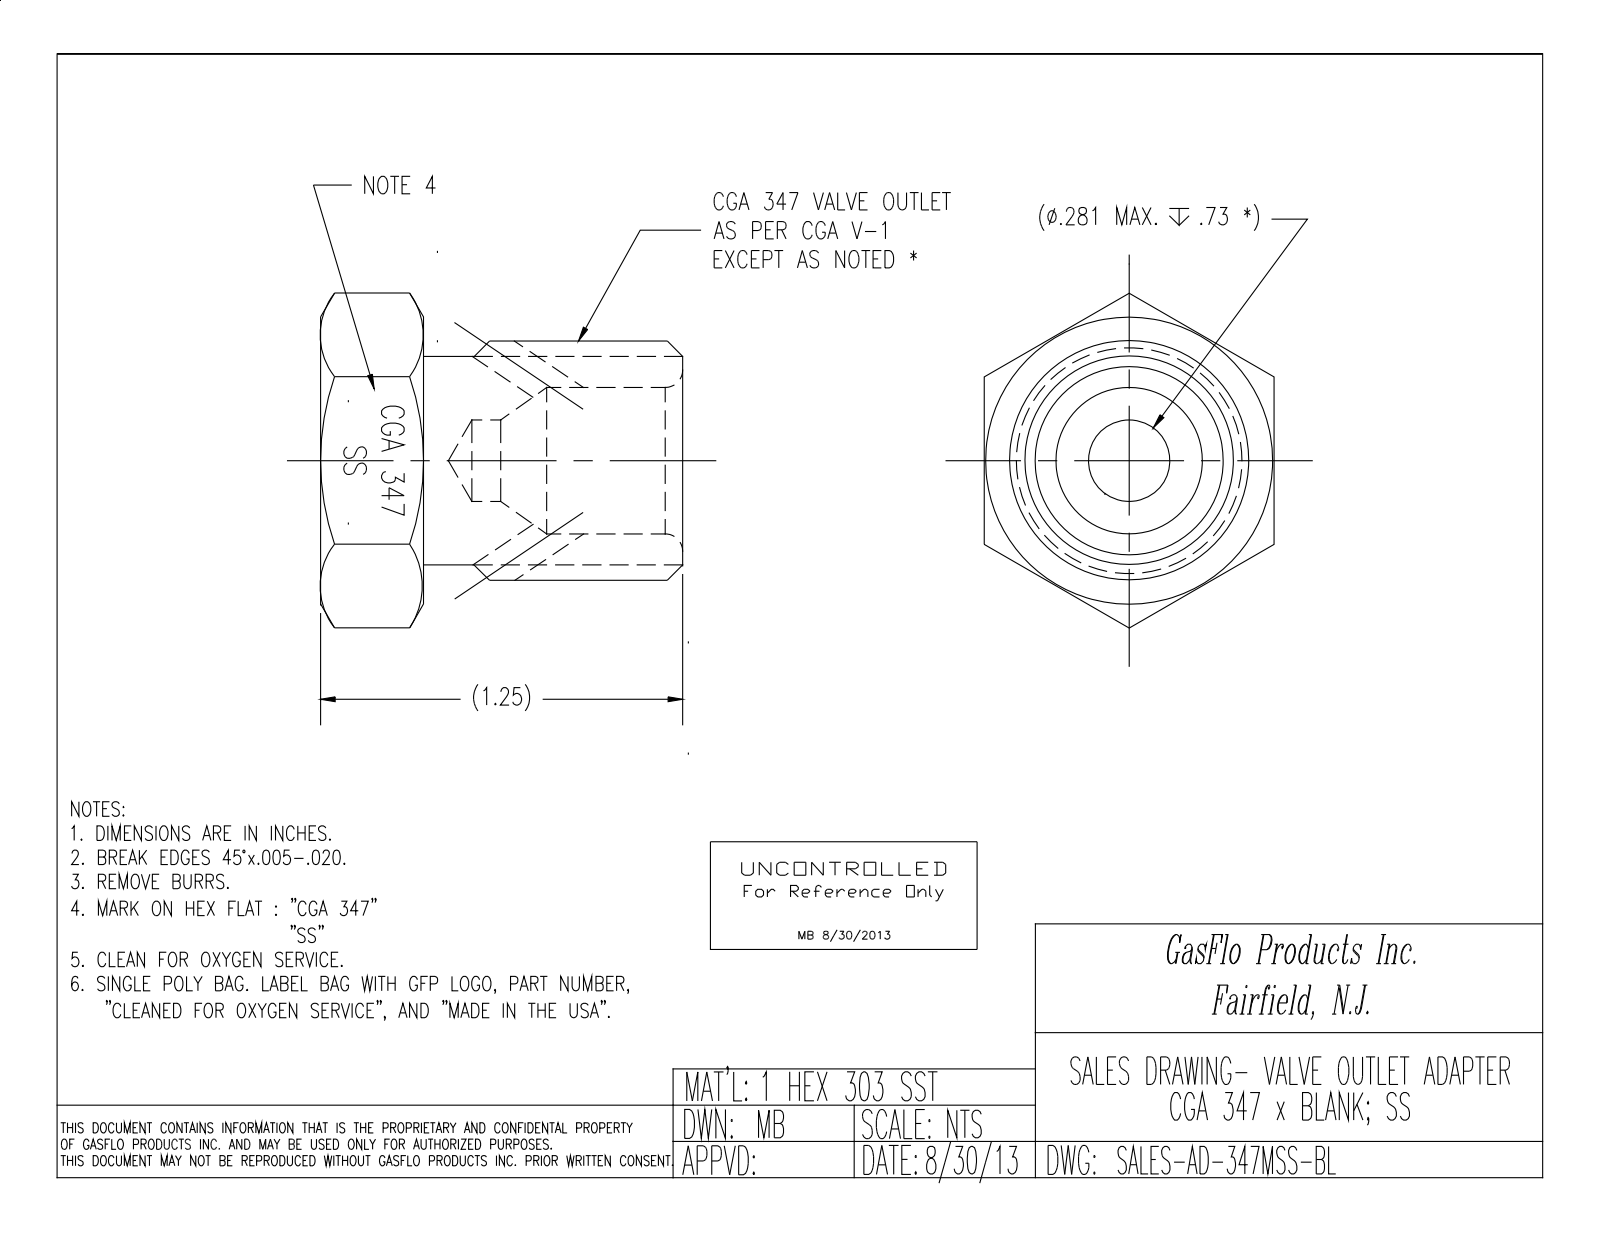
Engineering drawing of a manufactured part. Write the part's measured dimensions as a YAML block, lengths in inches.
part_name: "AD-347MSS-BL"
step_written_by: "SolidWorks 2018 (CONFIG_CONTROL_DESIGN)"
units: inches
bodies: {solids: 1, faces: 204, planar: 62, cylindrical: 53, other: 89}
overall_size: [1.25, 1.155, 1]
volume: 0.585
surface_area: 7.362
round_holes:
  - {diameter: 0.125, count: 2}
  - {diameter: 0.281, count: 1}
  - {diameter: 0.505, count: 1}
round_bosses_or_shafts:
  - {diameter: 0.823, count: 1}
  - {diameter: 0.723, count: 1}
  - {diameter: 0.72, count: 1}
face_to_face_distances: [1, 0.36, 1.25, 0.89, 0.99, 0.052, 0.045, 0.061, 0.279, 0.081]
